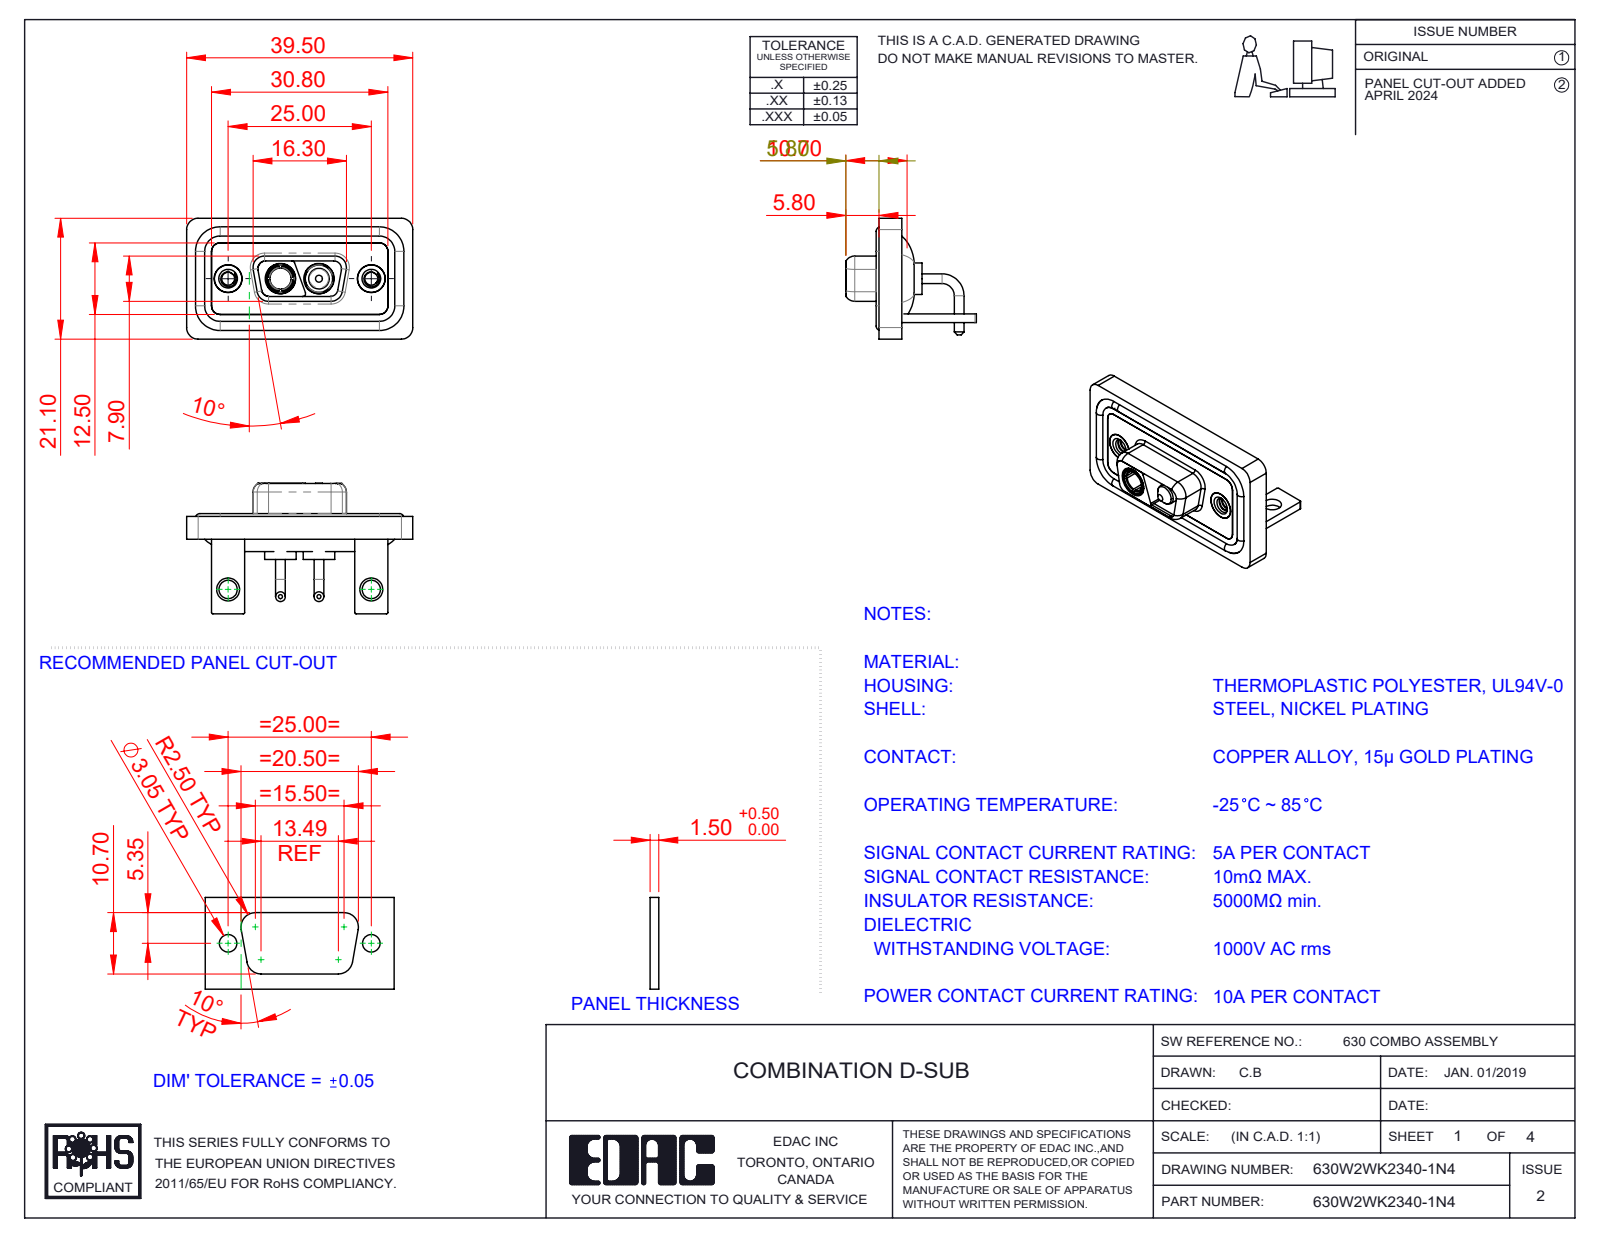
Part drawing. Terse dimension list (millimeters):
name: 630W2WK2340-1N4; 630Combo Threaded Rivet_2; 630Combo Shell Front_09 Contacts; Power Pin_10A RA (+5 more)
written by: SolidWorks 2023 (CONFIG_CONTROL_DESIGN)
unit: mm
bodies: 13 solids, 556 faces (164 planar, 259 cylindrical, 133 other)
size: 39.5 × 22.8 × 21.1
volume: 4 957 mm³; area: 8 128 mm²
holes: 4× ⌀4.85, 2× ⌀2.26, 2× ⌀3.2, 2× ⌀4, 2× ⌀4.05, 2× ⌀5, 2× ⌀5.3, 1× ⌀3.7
bosses: 4× ⌀1.7, 4× ⌀1.6, 2× ⌀5.5, 2× ⌀5.2, 2× ⌀4.95, 2× ⌀4.8, 2× ⌀4.75, 2× ⌀3.75
rounds: 19× R2, 18× R1.5, 16× R0.25, 8× R1.35, 8× R1.6, 7× R0.5, 4× R0.6, 4× R0.65
face distances: 0.4, 2.9, 1.5, 1.1, 3.7, 1.8, 0.8, 2.5, 1.6, 3.1
hole spacings: 9.14, 15.86, 25, 6.72
